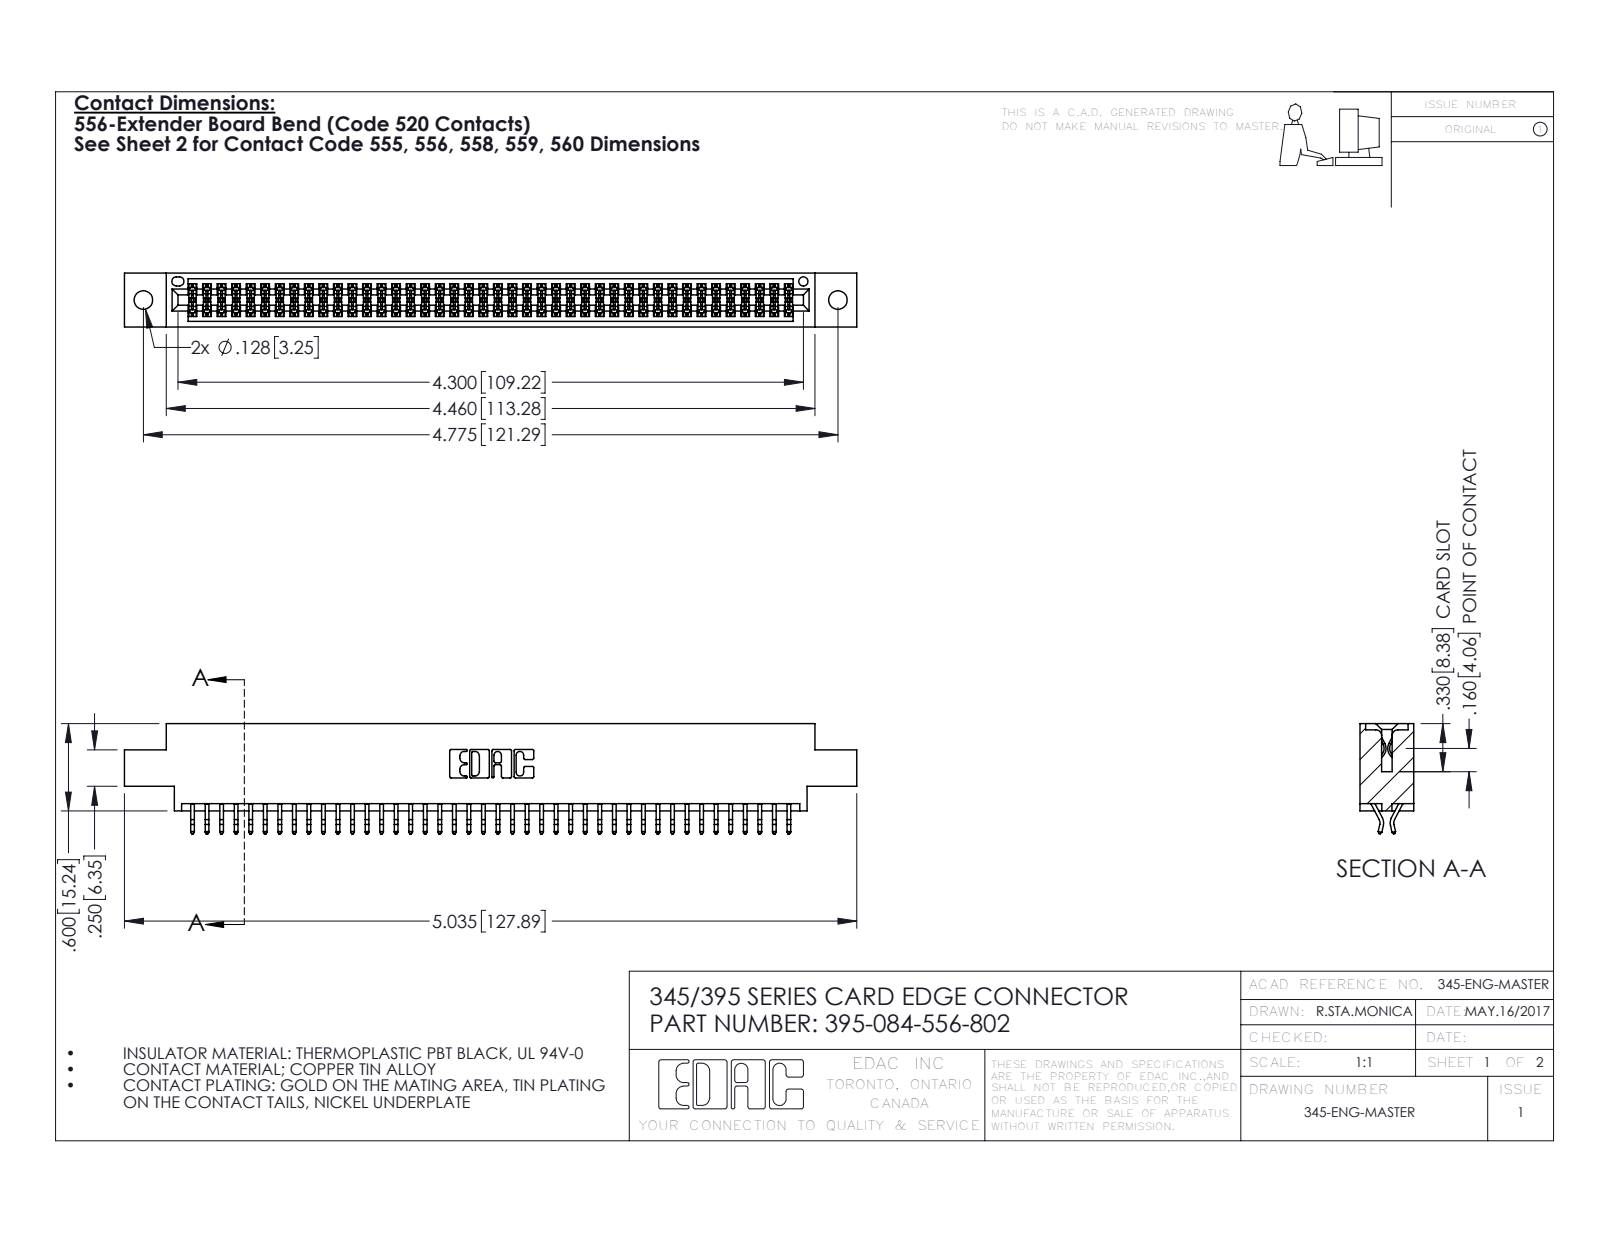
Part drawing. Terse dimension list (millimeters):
name: 395-084-556-802; 345-292-001_556 Tail; 345 Part_0.170 Offset - 0.128 Dia
written by: SolidWorks 2016 (CONFIG_CONTROL_DESIGN)
unit: mm
bodies: 85 solids, 4834 faces (3192 planar, 1642 cylindrical, 0 other)
size: 127.9 × 19.2 × 9.4
volume: 12 300 mm³; area: 17 940 mm²
holes: 2× ⌀3.3, 1× ⌀1.6
rounds: 126× R0.2, 22× R0.3, 6× R0.2, 6× R0.8, 3× R0.7, 2× R0.3, 2× R0.4, 2× R0.5
face distances: 7.6, 1.8, 9.4, 5.1, 0.6, 2.5, 6.9, 5.7, 4.4, 3.8
hole spacings: 6.9, 115.3, 121.3
